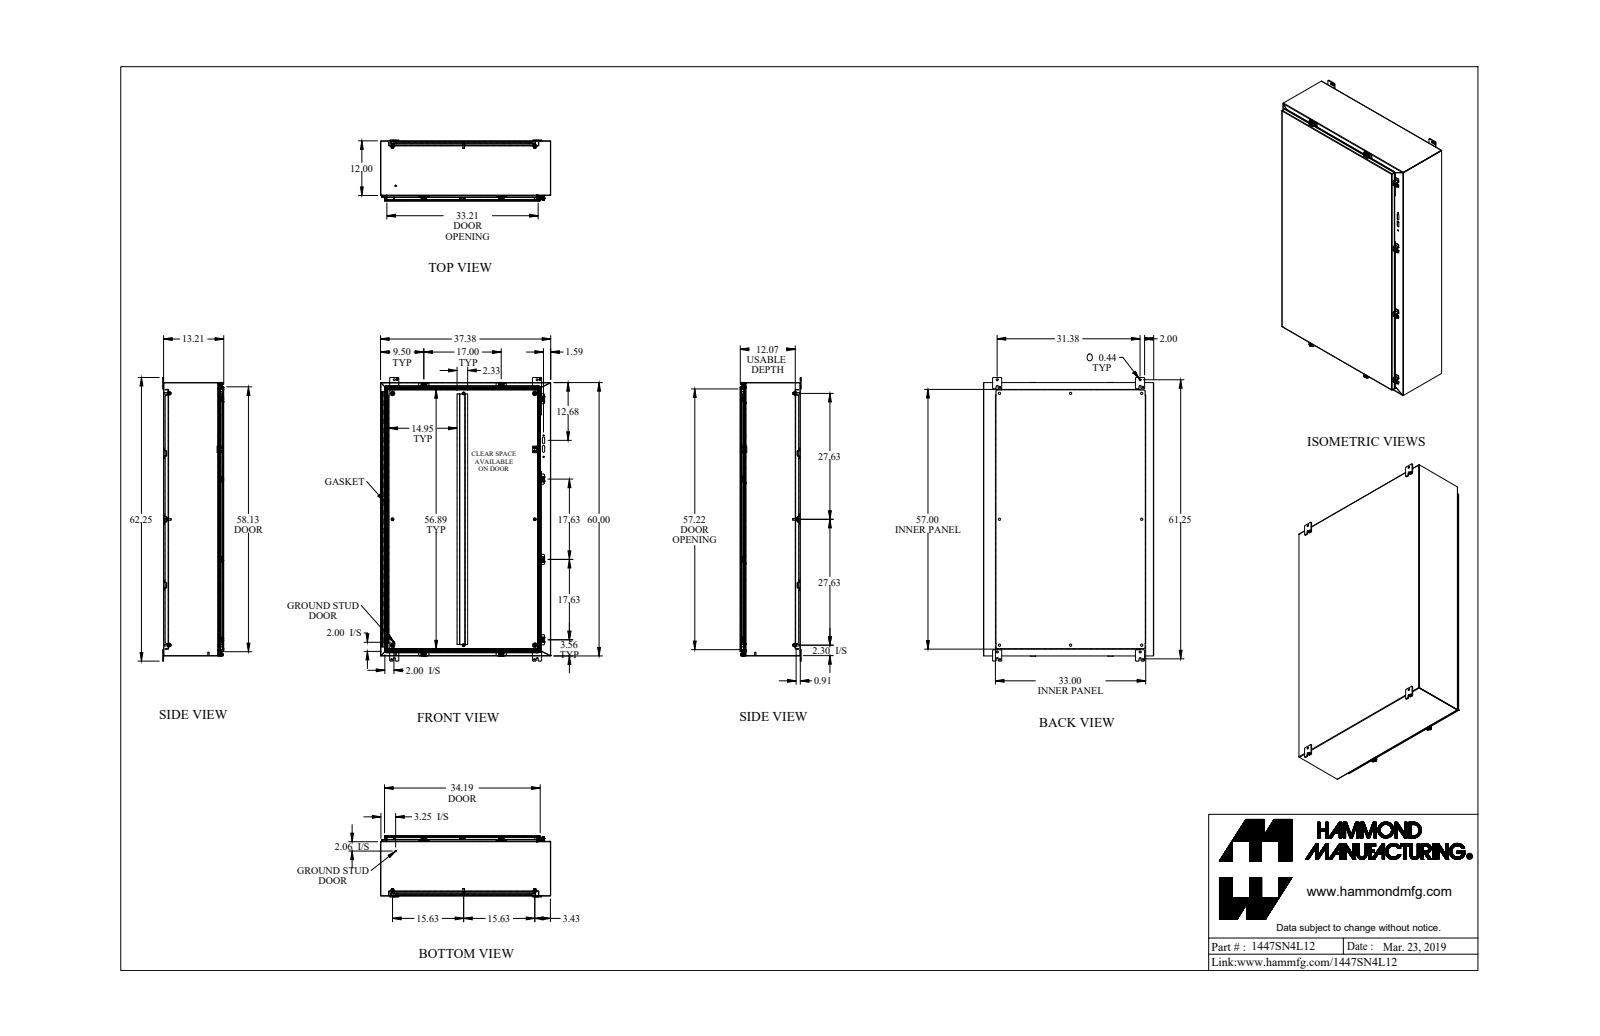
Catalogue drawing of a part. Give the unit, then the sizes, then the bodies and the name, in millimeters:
Units: millimetres
Overall size (bounding box): 1581.2 × 949.3 × 340.3
Round holes (diameter × count): ⌀5.4 ×8, ⌀6.7 ×8, ⌀9.5 ×8, ⌀12.7 ×8, ⌀8 ×6, ⌀7.8 ×4, ⌀11.1 ×4, ⌀11.3 ×4, ⌀3.8 ×2, ⌀4 ×2, ⌀7.1 ×2, ⌀4.7 ×1
Round bosses / shafts (diameter × count): ⌀16.5 ×8, ⌀12.7 ×8, ⌀9.9 ×8, ⌀8.4 ×8, ⌀6.2 ×8, ⌀9.5 ×7, ⌀25.4 ×4, ⌀6.4 ×4
Partial cylindrical surfaces — rounded edges, fillets, slot ends (radius × count): R6.4 ×48, R1.2 ×39, R3.6 ×39, R4.8 ×32, R0.9 ×21, R2.7 ×21, R2.9 ×16, R3.6 ×16
Main face-to-face distances: 1.8, 331.9, 333.7, 1.8, 333.7, 335.5, 2.4, 307.5, 305.7, 26.2
Hole centre spacings: 793.8, 701.7, 796.9, 1059.4, 1458.4, 1612.3, 182.8, 194.9
Volume: 12 750 000 mm³ · Surface area: 13 130 000 mm²
Bodies: 72 solids, 2529 faces (1456 planar, 941 cylindrical, 132 other)
Part name (STEP PRODUCT): 1447SN4L12_Default
STEP written by: SolidWorks 2019 (CONFIG_CONTROL_DESIGN)
